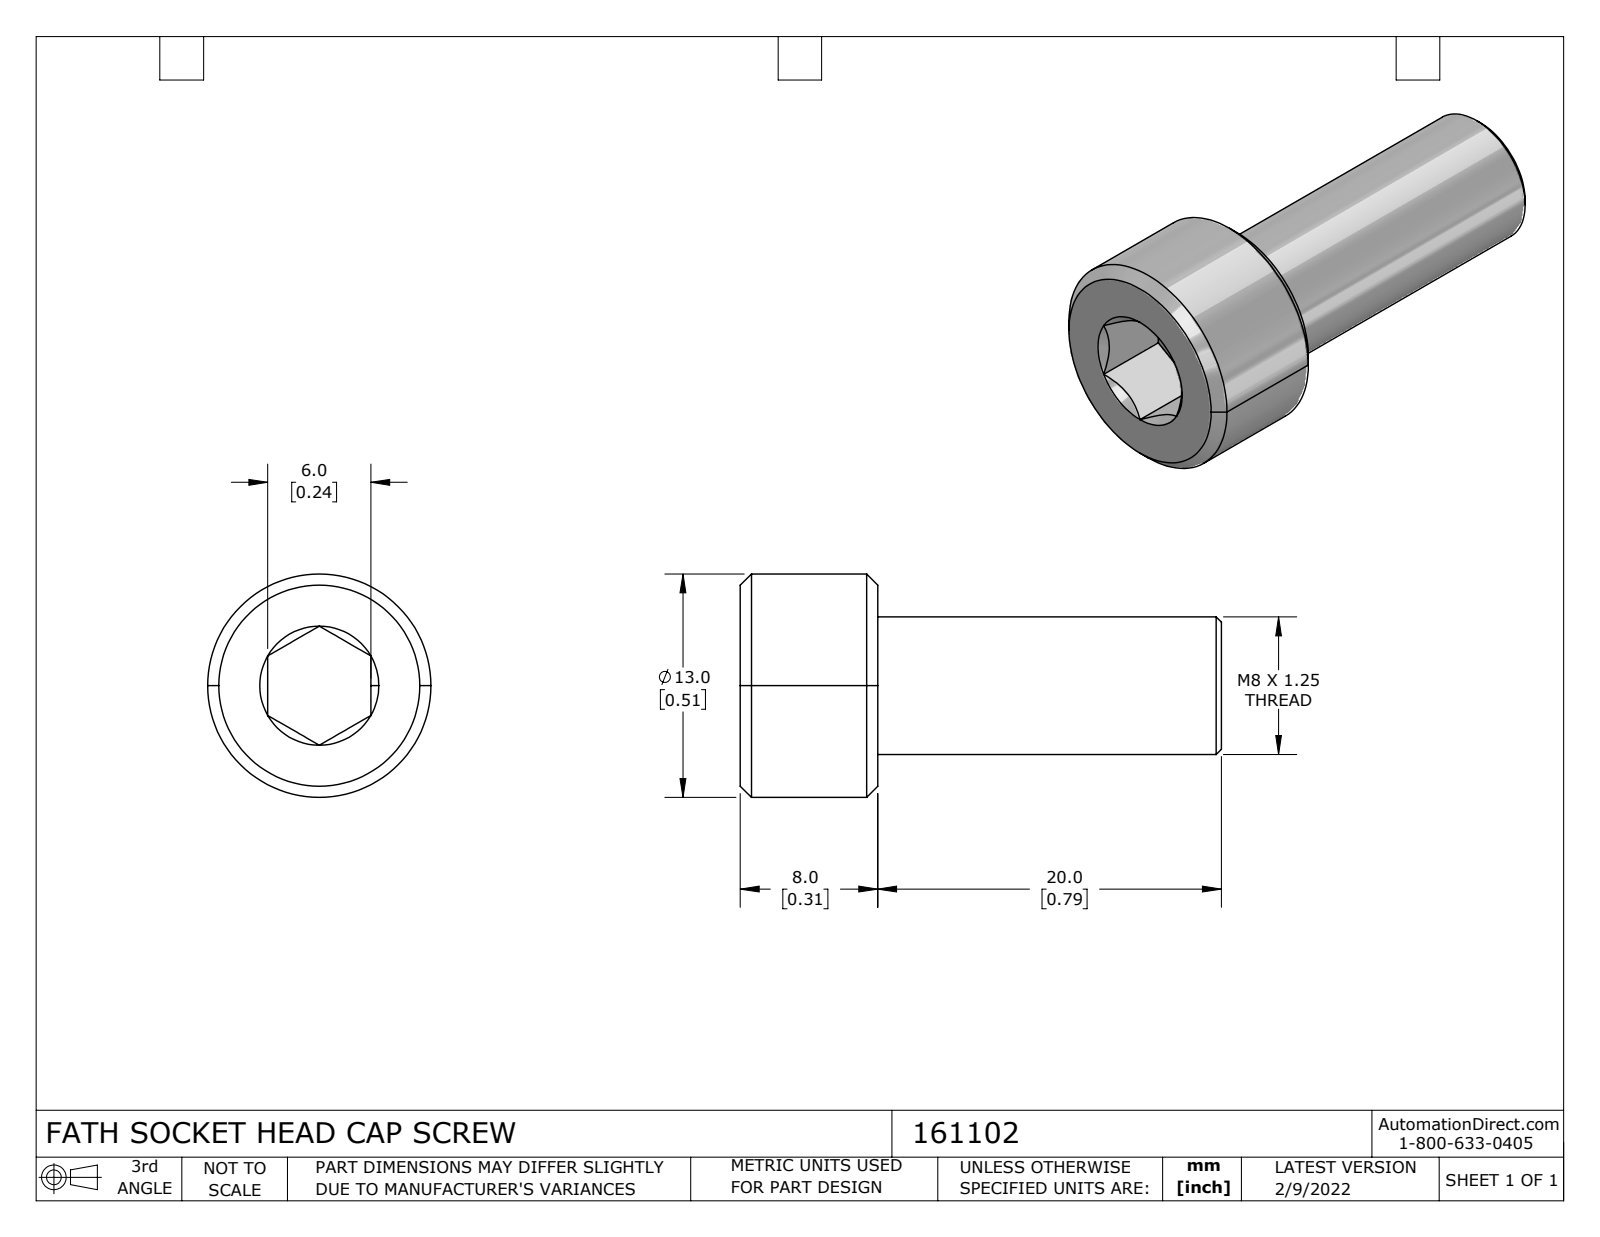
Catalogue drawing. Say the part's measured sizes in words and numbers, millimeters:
The part is named "161102". Its 3-D file was written by "SolidWorks 2021 (CONFIG_CONTROL_DESIGN)". It is 1 solid with 27 faces: 10 planar, 4 cylindrical and 13 other. Overall it measures 28 by 13 by 13 millimeters. Its volume is 1 908 cubic millimeters and its surface area 1 148 square millimeters. Round bosses or shafts: 1 of diameter 13, 1 of diameter 8. The main face-to-face distances are 8, 6, 28, 20, 4.5, 3.5, 23.5.
